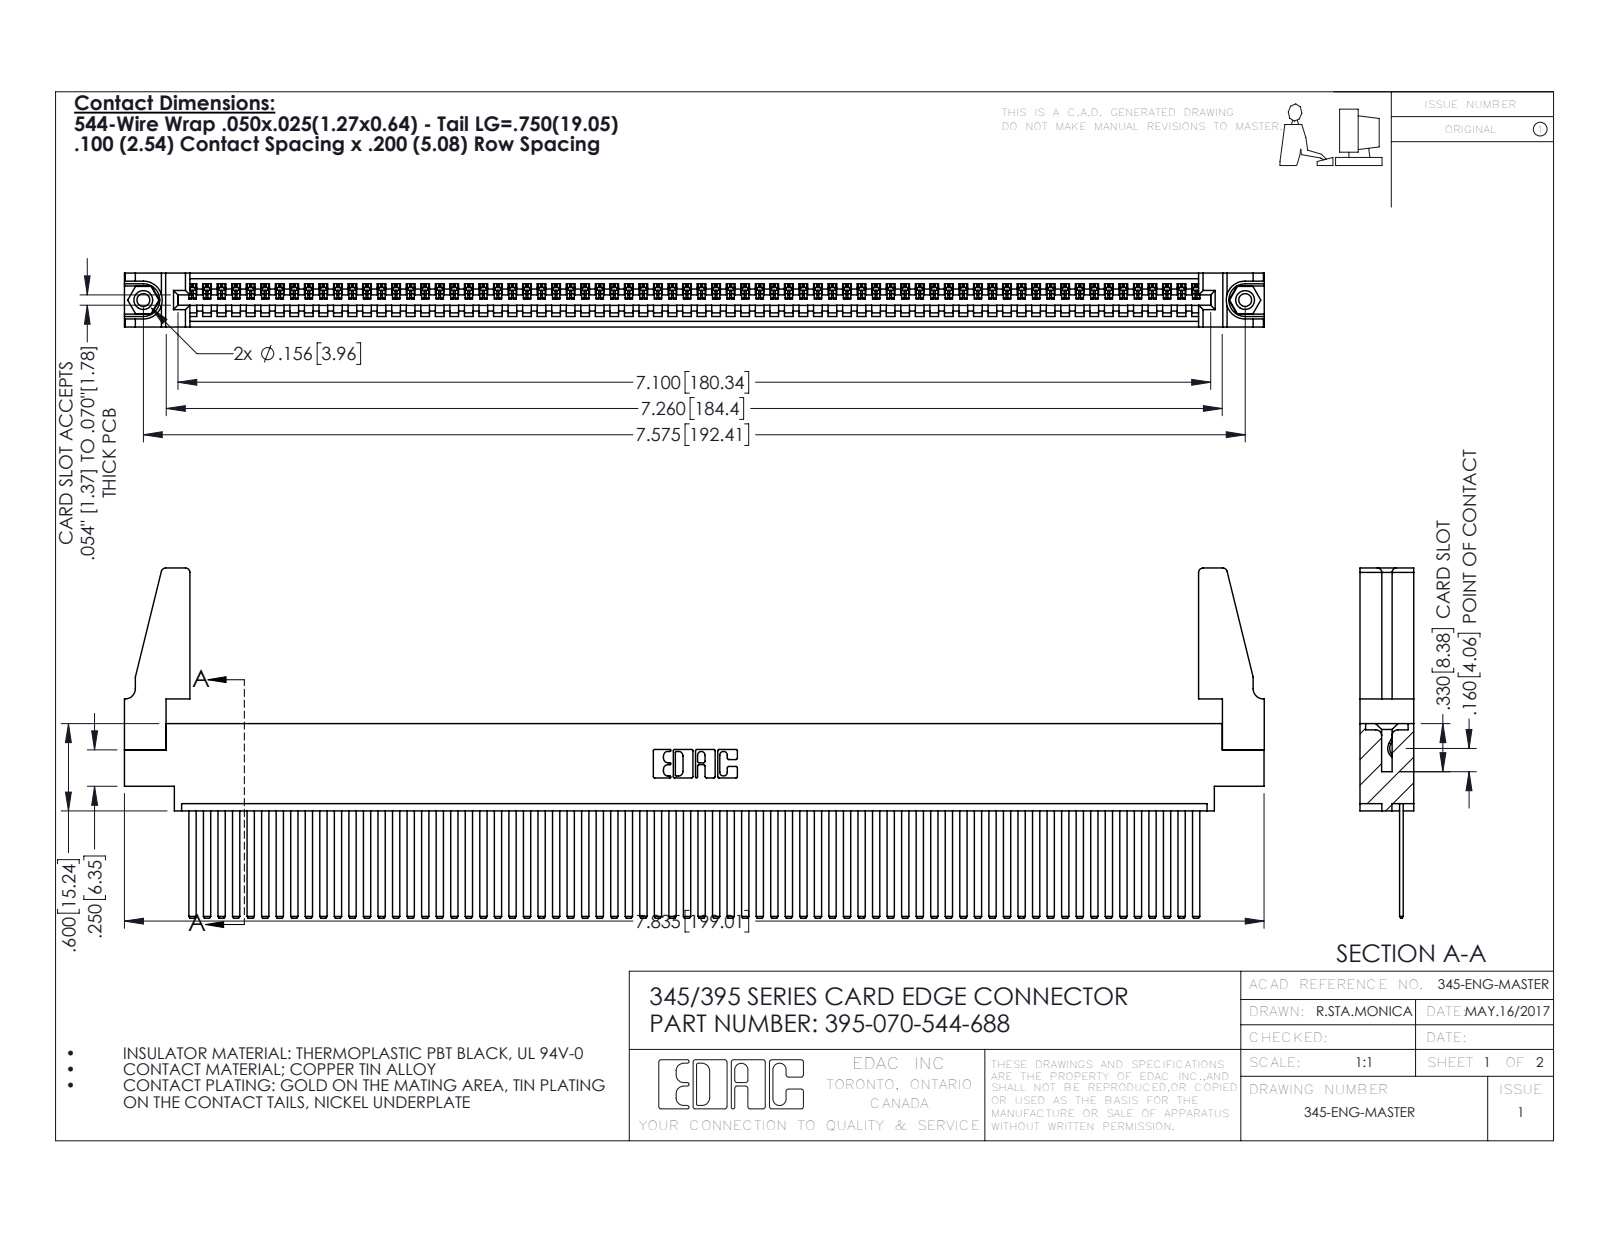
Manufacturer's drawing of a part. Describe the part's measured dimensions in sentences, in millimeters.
The part is named "345-220-078_345-220-088; 345-250-001_345-250-001-102; 395-070-544-688; 345-292-001_345-293-144 (+1 more)". Its 3-D file was written by "SolidWorks 2016 (CONFIG_CONTROL_DESIGN)". It is 75 solids with 3894 faces: 2676 planar, 1202 cylindrical and 16 other. Overall it measures 199 by 61.1 by 9.4 millimeters. Its volume is 23 090 cubic millimeters and its surface area 32 430 square millimeters. Round holes: 2 of diameter 2.3, 2 of diameter 3.2, 2 of diameter 4, 1 of diameter 1.6. Round bosses or shafts: 2 of diameter 3.9. Partial cylindrical surfaces (rounded edges, fillets, slot ends): 140 of radius 0.2, 22 of radius 0.3, 8 of radius 0.8, 6 of radius 0.2, 6 of radius 0.8, 3 of radius 0.7, 2 of radius 0.8, 2 of radius 1. The main face-to-face distances are 1.8, 7.6, 2.5, 6.9, 0.6, 9.4, 5.1, 5.7, 4.4, 3.8. The hole center spacings are 6.9, 186.4, 192.4.
